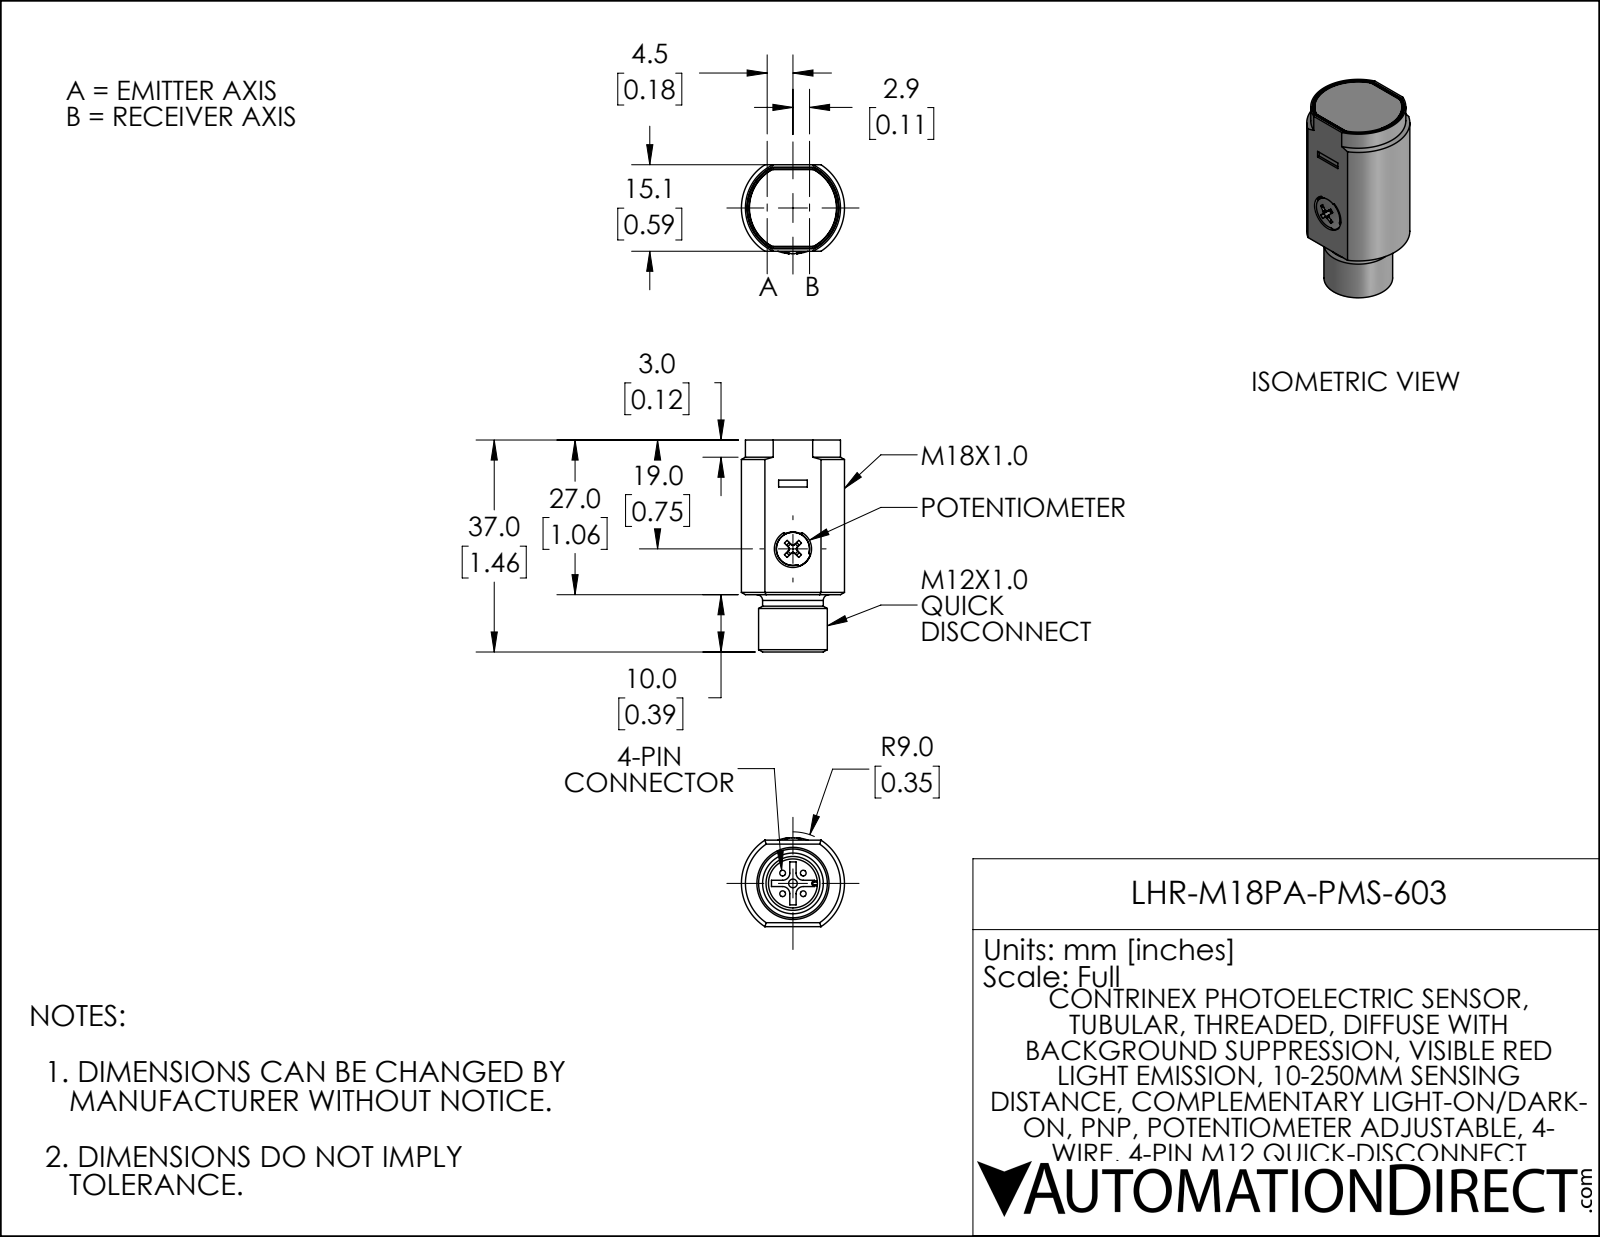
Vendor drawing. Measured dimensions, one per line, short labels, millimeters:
name: LHR-M18PA-PMS-603
written by: SolidWorks 2021 (AUTOMOTIVE_DESIGN)
unit: mm
bodies: 1 solid, 148 faces (75 planar, 53 cylindrical, 20 other)
size: 37 × 18 × 15.5
volume: 6 830 mm³; area: 2 756 mm²
holes: 1× ⌀1.5, 1× ⌀6.5, 1× ⌀8.5
bosses: 4× ⌀1, 1× ⌀12, 1× ⌀10.6
rounds: 8× R0.4, 8× R0.7, 4× R0.2, 4× R0.6, 4× R1.2, 2× R0.2, 1× R0.4, 1× R2.9
face distances: 15.1, 26.9, 1.2, 28.1, 0.4, 27, 28.2, 37, 37, 10
